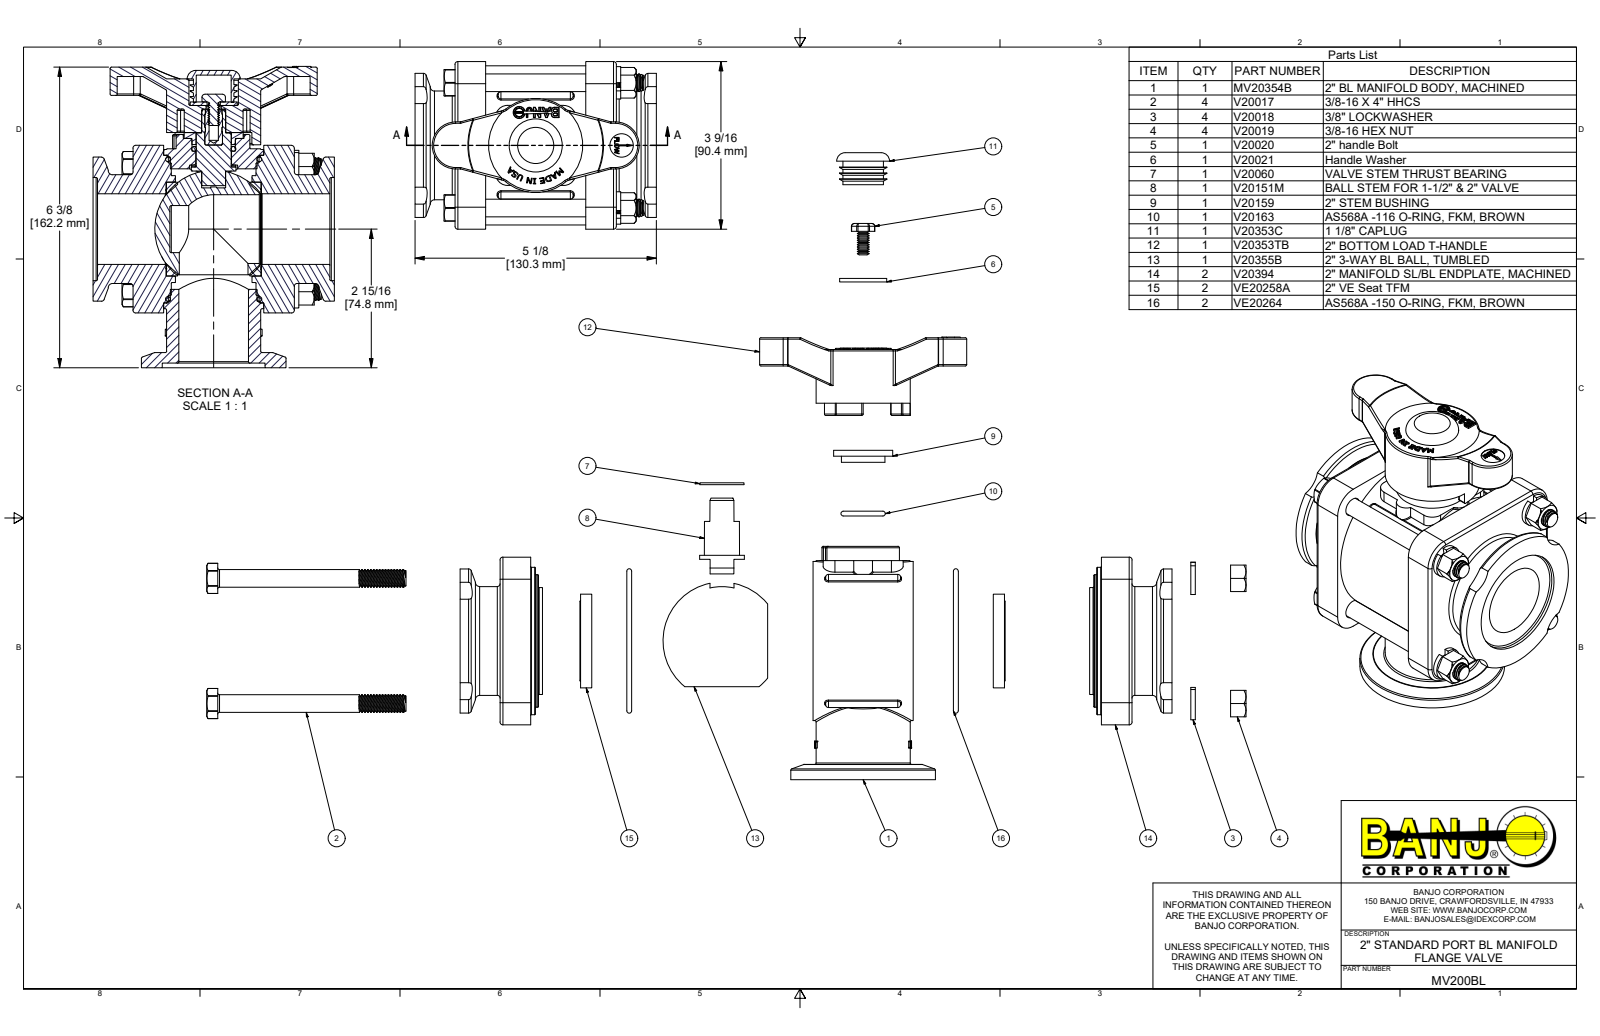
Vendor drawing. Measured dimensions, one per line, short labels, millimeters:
name: MV200BL; MV20354B; MV20354BX; V20151M (+8 more)
written by: Autodesk Inventor 2022 (AUTOMOTIVE_DESIGN)
unit: mm
bodies: 30 solids, 2832 faces (1333 planar, 565 cylindrical, 934 other)
size: 162.6 × 130.3 × 90.4
volume: 694 500 mm³; area: 202 100 mm²
holes: 4× ⌀7.8, 4× ⌀9.8, 4× ⌀10.3, 2× ⌀37.1, 1× ⌀4.4, 1× ⌀5, 1× ⌀5.8, 1× ⌀6.2, 1× ⌀7.1, 1× ⌀8.1, 1× ⌀8.2, 1× ⌀8.9
bosses: 60× ⌀8.2, 4× ⌀17.4, 4× ⌀9.5, 1× ⌀85.9, 1× ⌀79.5, 1× ⌀78.1, 1× ⌀71.4, 1× ⌀58.7
rounds: 61× R0.8, 14× R1.5, 8× R0.5, 8× R1.9, 8× R4.1, 4× R1.6, 4× R2.3, 4× R3.2
face distances: 16.5, 70.6, 21.6, 87.1, 38.1, 92.2, 108.7, 90.4, 54.1, 1.3
hole spacings: 47.8, 67.5, 95.5, 19.9, 46.4, 58
